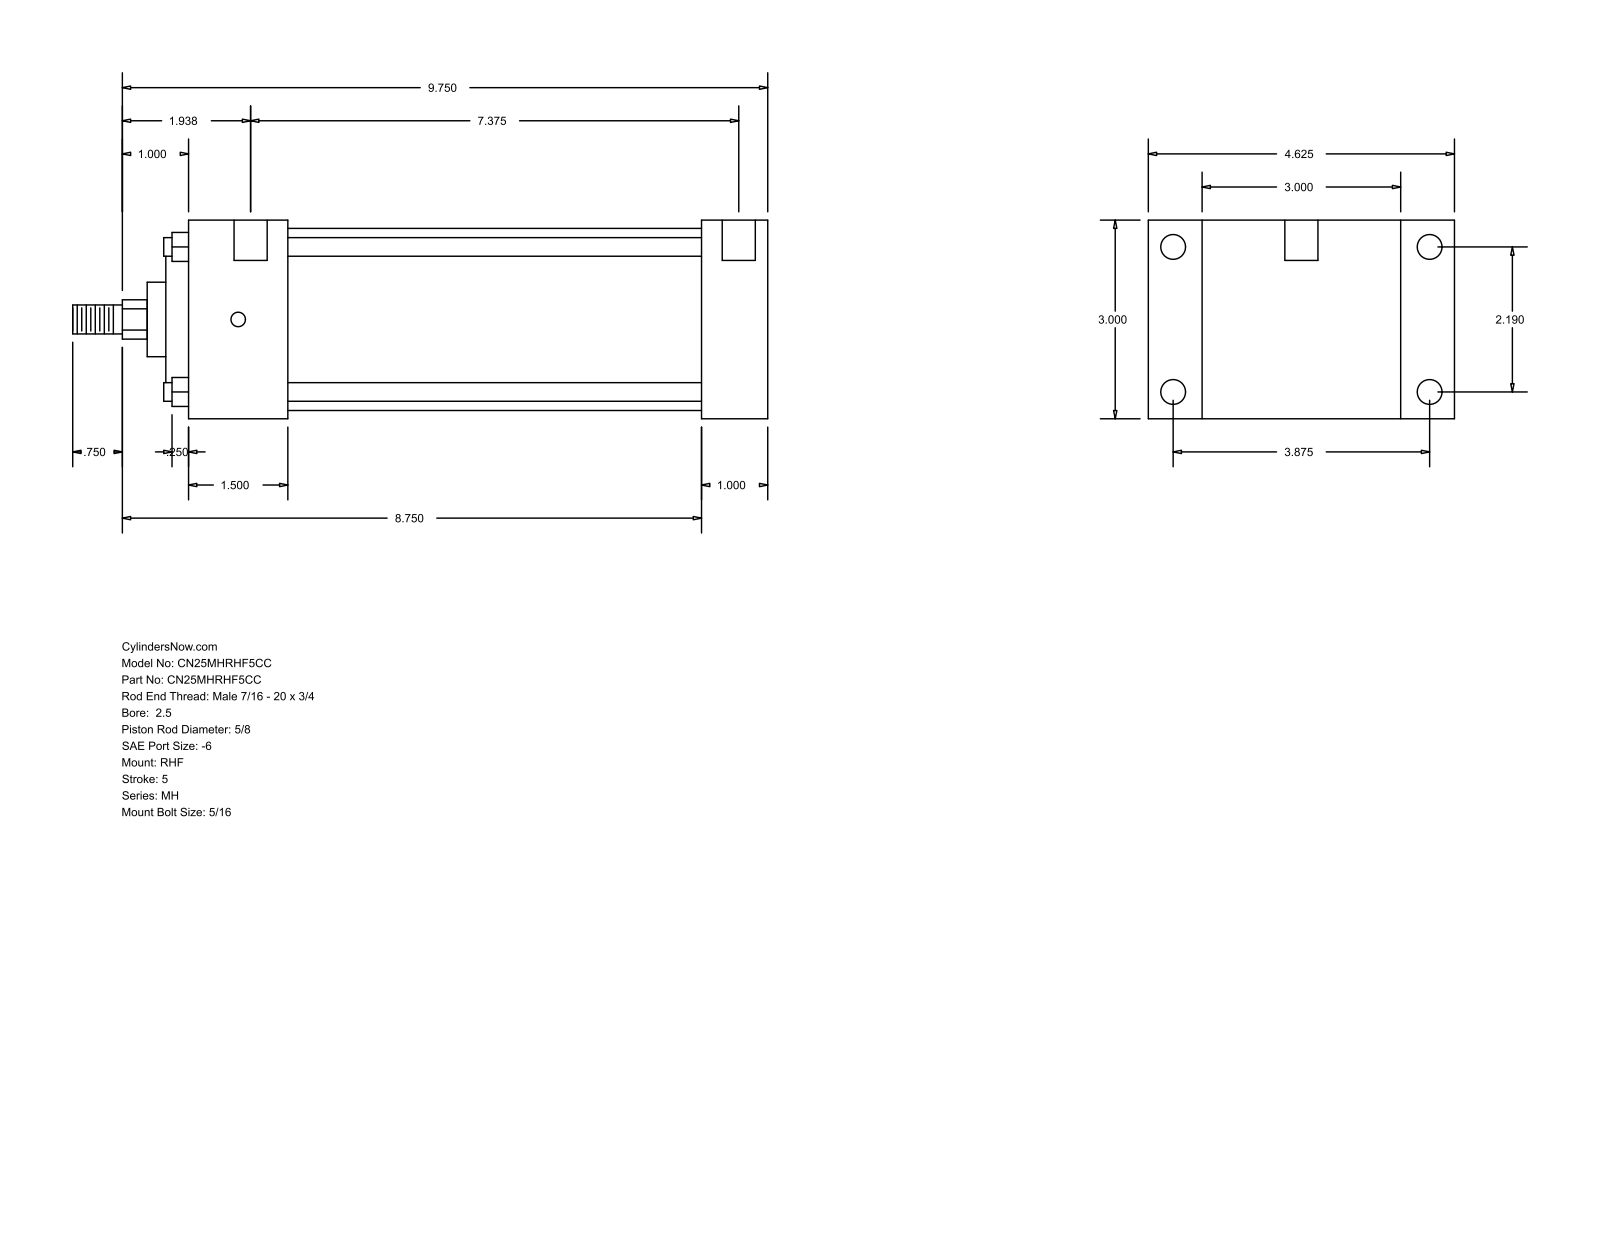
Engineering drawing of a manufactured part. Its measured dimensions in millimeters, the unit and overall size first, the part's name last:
Units: millimetres
Overall size (bounding box): 266.7 × 117.47 × 76.2
Round holes (diameter × count): ⌀5.56 ×4, ⌀9.53 ×4, ⌀12.7 ×2
Round bosses / shafts (diameter × count): ⌀7.14 ×4, ⌀69.85 ×1, ⌀55.55 ×1, ⌀28.57 ×1, ⌀15.88 ×1, ⌀11.11 ×1
Partial cylindrical surfaces — rounded edges, fillets, slot ends (radius × count): R7.54 ×1
Main face-to-face distances: 76.2, 25.4, 20.64, 96.84, 222.25, 196.85, 38.1, 117.48, 158.75, 184.15
Hole centre spacings: 55.62, 98.42, 113.05, 195.26, 3.17, 4.76, 187.33, 190.5
Bodies: 0 solids, 90 faces (61 planar, 29 cylindrical, 0 other)
Part name (STEP PRODUCT): MH_RHF__0250_0.625
STEP written by: GSSL Pune (CONFIG_CONTROL_DESIGN)
